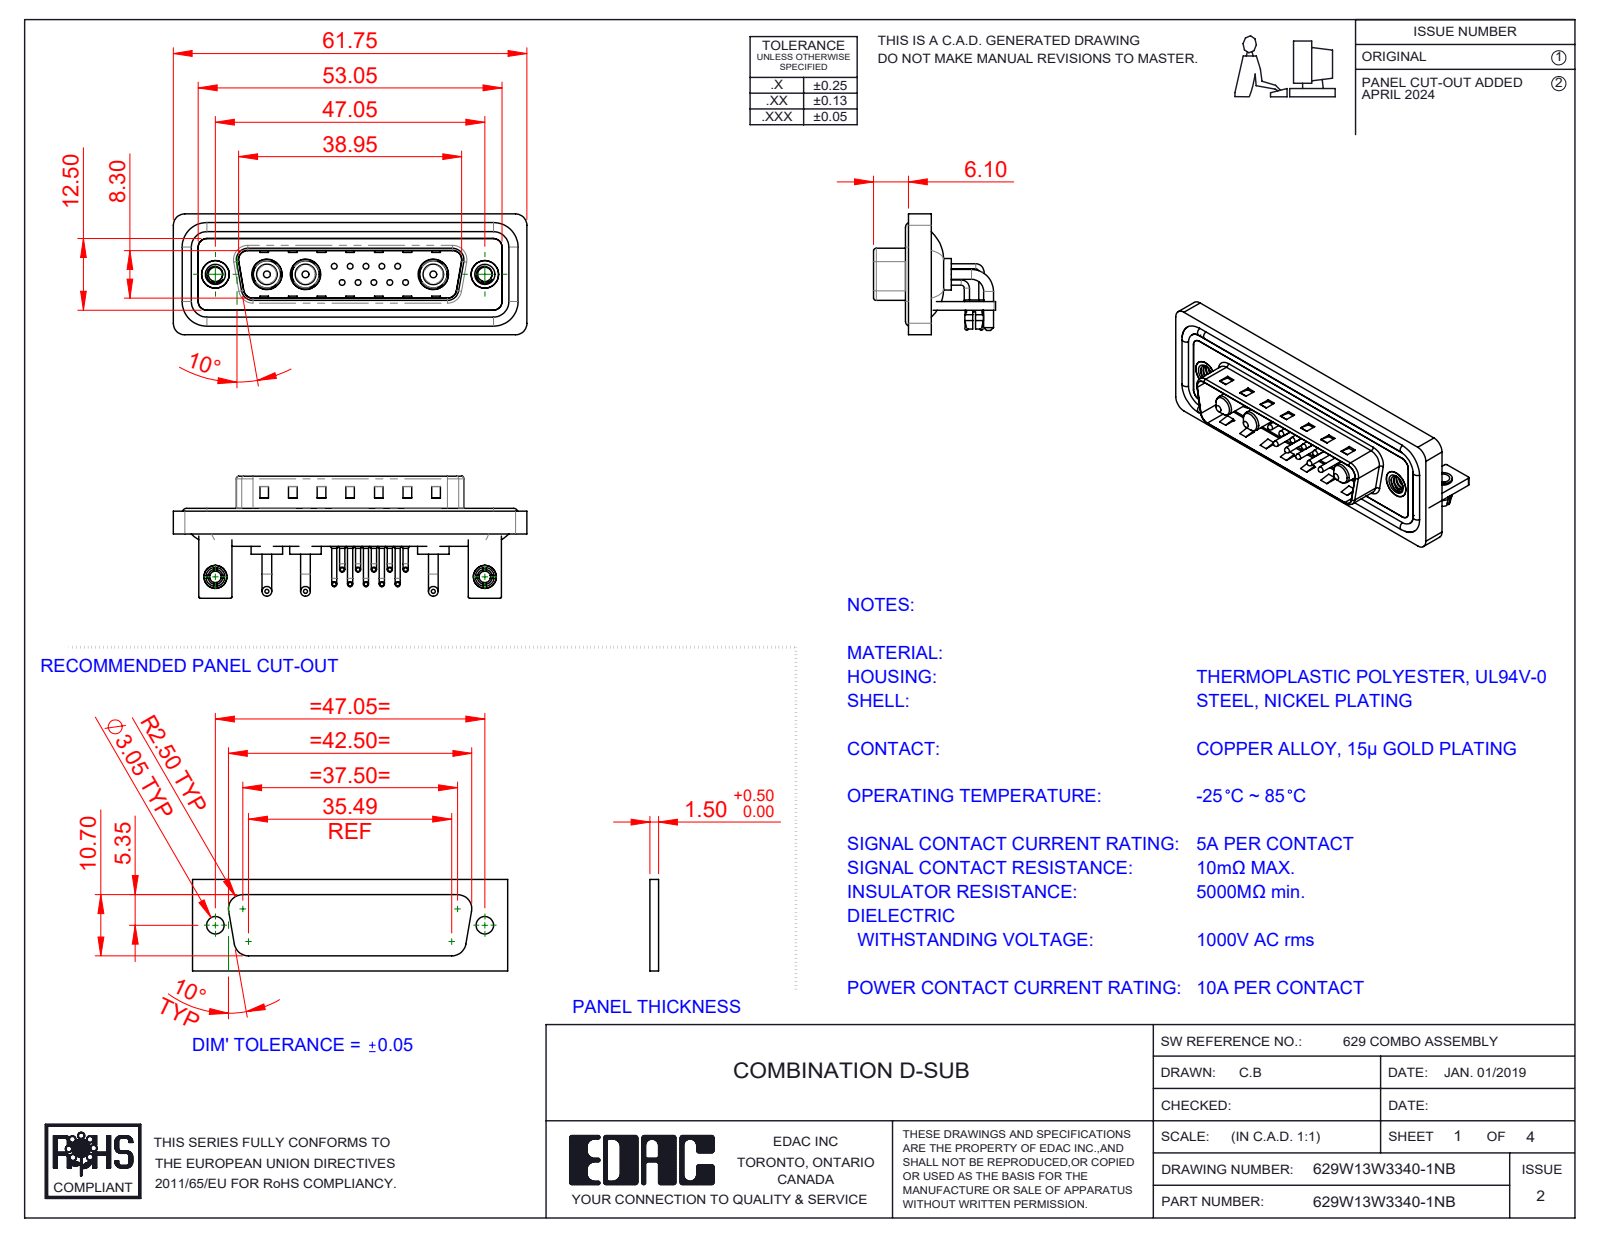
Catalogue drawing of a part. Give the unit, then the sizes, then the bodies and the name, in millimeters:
Units: millimetres
Overall size (bounding box): 61.75 × 21.3 × 21.1
Round holes (diameter × count): ⌀2 ×12, ⌀0.75 ×10, ⌀1.6 ×10, ⌀2.5 ×4, ⌀4.85 ×3, ⌀5.3 ×3, ⌀3.2 ×2, ⌀4 ×2, ⌀4.8 ×2, ⌀5 ×2
Round bosses / shafts (diameter × count): ⌀0.9 ×20, ⌀1.5 ×10, ⌀1 ×10, ⌀0.65 ×10, ⌀1.7 ×6, ⌀1.6 ×4, ⌀5.5 ×3, ⌀5.2 ×3
Partial cylindrical surfaces — rounded edges, fillets, slot ends (radius × count): R2 ×19, R1.5 ×18, R0.25 ×16, R1.01 ×10, R0.5 ×9, R1.6 ×8, R0.6 ×4, R0.65 ×4
Main face-to-face distances: 0.4, 1.5, 0.8, 2.9, 2.1, 1.1, 4.1, 1.6, 3.7, 4.5
Hole centre spacings: 3.16, 2.77, 5.04, 5.54, 7.49, 5.03, 8.31, 10.11
Volume: 7 744 mm³ · Surface area: 13 142 mm²
Bodies: 27 solids, 1842 faces (947 planar, 661 cylindrical, 234 other)
Part name (STEP PRODUCT): 629Combo Shell Rear_25 Contacts; Power Pin_10A RA; 629W13W3340-1NB; 629Combo Contact Row 1 (+7 more)
STEP written by: SolidWorks 2023 (CONFIG_CONTROL_DESIGN)
